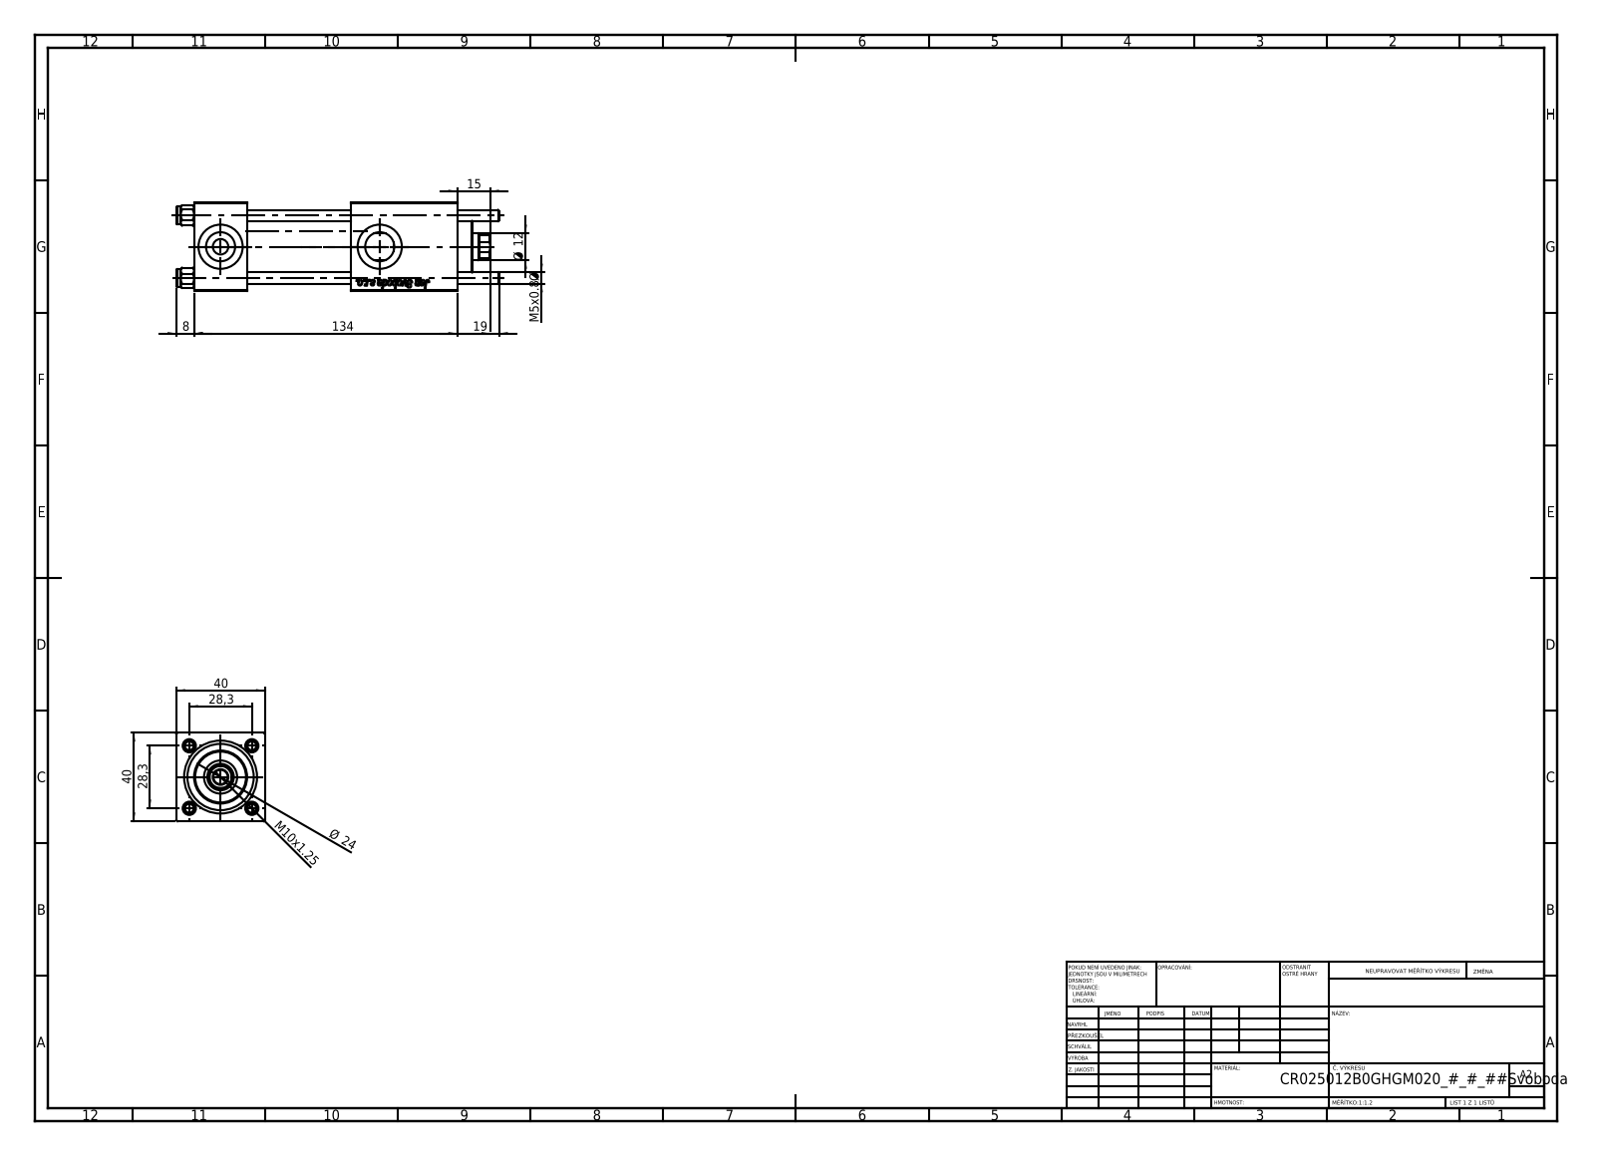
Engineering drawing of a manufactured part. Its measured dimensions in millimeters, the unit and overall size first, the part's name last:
Units: millimetres
Overall size (bounding box): 146 × 40 × 40
Round holes (diameter × count): ⌀5 ×4, ⌀20 ×3, ⌀7 ×2, ⌀13.16 ×2, ⌀6.5 ×1, ⌀12 ×1, ⌀15 ×1, ⌀25 ×1, ⌀30 ×1
Round bosses / shafts (diameter × count): ⌀8 ×4, ⌀31 ×1, ⌀24 ×1
Partial cylindrical surfaces — rounded edges, fillets, slot ends (radius × count): R5.5 ×1
Main face-to-face distances: 40, 24, 90.3, 66.3, 71, 47, 19.3, 119, 95, 48
Hole centre spacings: 20.01, 28.3, 40.02, 72
Volume: 144 884 mm³ · Surface area: 58 619 mm²
Bodies: 11 solids, 1155 faces (429 planar, 78 cylindrical, 648 other)
Part name (STEP PRODUCT): V215CR_VCP_B; V215CR_B_TYCINKA; V215_VC_A; V215CR_B-1 (+1 more)
STEP written by: SolidWorks 2019 (CONFIG_CONTROL_DESIGN)
